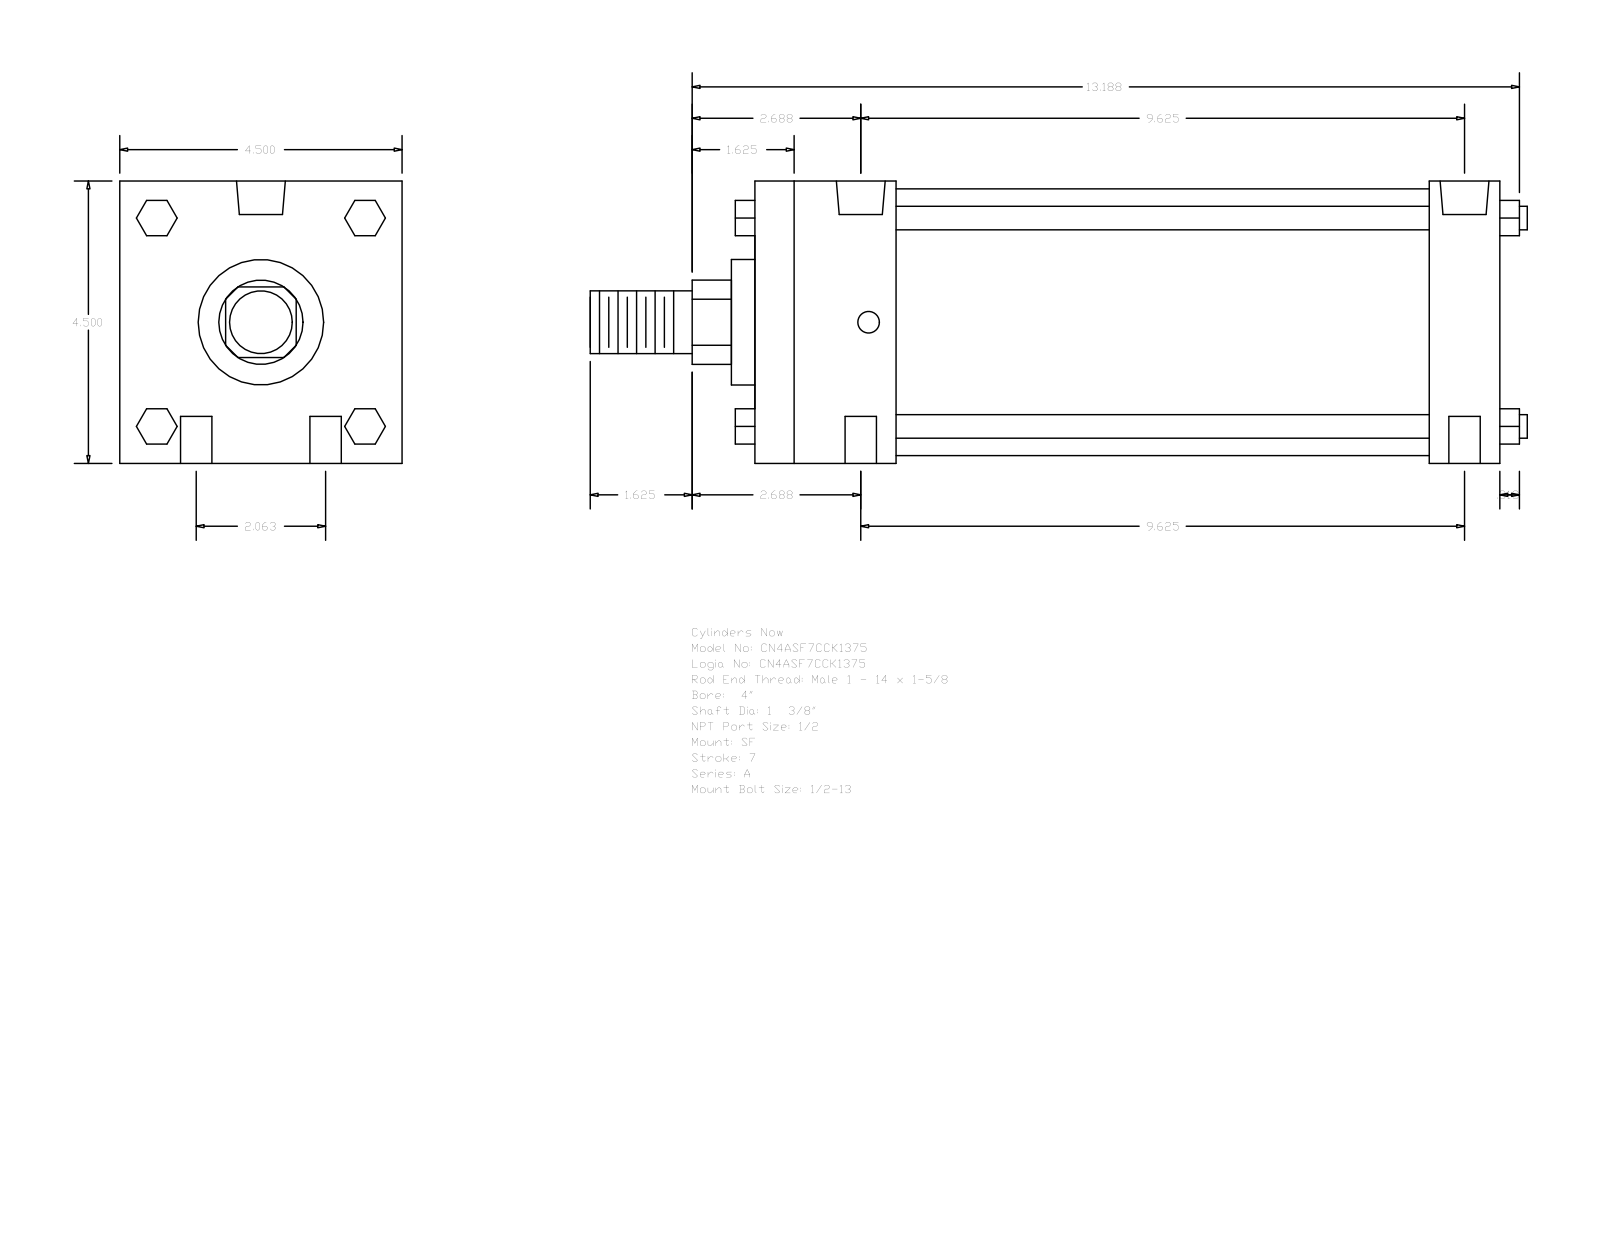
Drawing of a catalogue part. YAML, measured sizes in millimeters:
part_name: "A_SF__0400_1.375"
step_written_by: "GSSL Pune (CONFIG_CONTROL_DESIGN)"
units: millimeters
bodies: {solids: 0, faces: 124, planar: 94, cylindrical: 30, other: 0}
overall_size: [379.41, 114.3, 114.3]
round_holes:
  - {diameter: 12.7, count: 4}
  - {diameter: 8.73, count: 2}
  - {diameter: 19.77, count: 2}
round_bosses_or_shafts:
  - {diameter: 9.53, count: 4}
  - {diameter: 107.95, count: 1}
  - {diameter: 50.8, count: 1}
  - {diameter: 34.92, count: 1}
  - {diameter: 25.4, count: 1}
partial_cylinders:
  - {radius: 17.06, count: 1}
face_to_face_distances: [114.3, 301.62, 57.15, 273.05, 28.57, 215.9, 244.47, 66.67, 14.29, 9.52]
hole_center_spacings: [26.19, 245.88, 244.48, 52.38, 250.03, 238.12]
